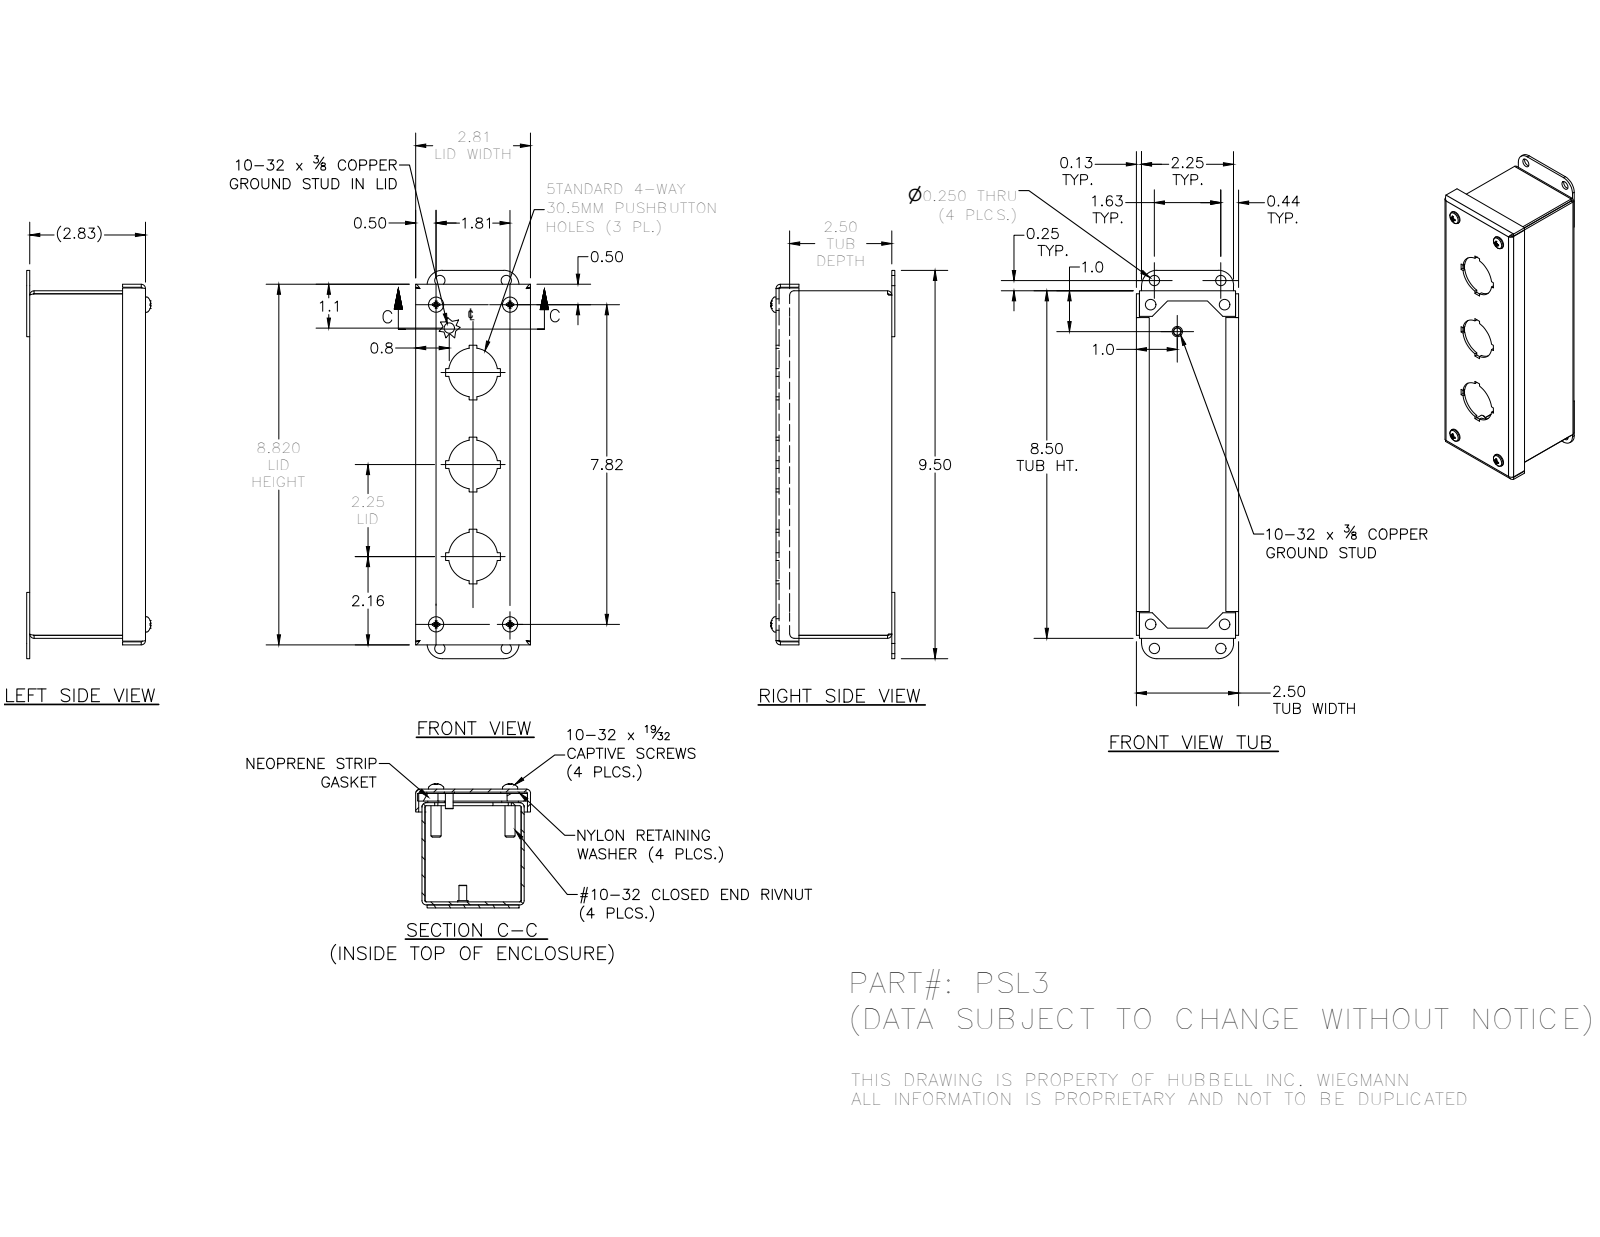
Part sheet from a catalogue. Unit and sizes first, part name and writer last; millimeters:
Units: millimetres
Overall size (bounding box): 241.3 × 77.11 × 71.37
Round holes (diameter × count): ⌀3.96 ×4, ⌀4.98 ×4, ⌀6.35 ×4, ⌀6.53 ×4, ⌀7.06 ×4, ⌀7.14 ×4, ⌀7.95 ×4, ⌀30.48 ×3
Round bosses / shafts (diameter × count): ⌀4.83 ×6, ⌀11.51 ×4, ⌀10.31 ×4, ⌀9.47 ×4, ⌀6.3 ×4, ⌀6.35 ×2
Partial cylindrical surfaces — rounded edges, fillets, slot ends (radius × count): R0.79 ×12, R2.67 ×12, R2.27 ×4, R9.53 ×4
Main face-to-face distances: 1.88, 61.62, 70.05, 63.5, 71.93, 59.74, 68.17, 4.78, 7.47, 2.69
Hole centre spacings: 116.15, 172.69, 48.02, 101.94, 158.14, 203.88, 15.16, 15.17
Volume: 177 597 mm³ · Surface area: 179 964 mm²
Bodies: 20 solids, 536 faces (314 planar, 108 cylindrical, 114 other)
Part name (STEP PRODUCT): PSL3LID; 372163; 39077; PSL3BKP (+5 more)
STEP written by: Autodesk Inventor 2016 (AUTOMOTIVE_DESIGN)
